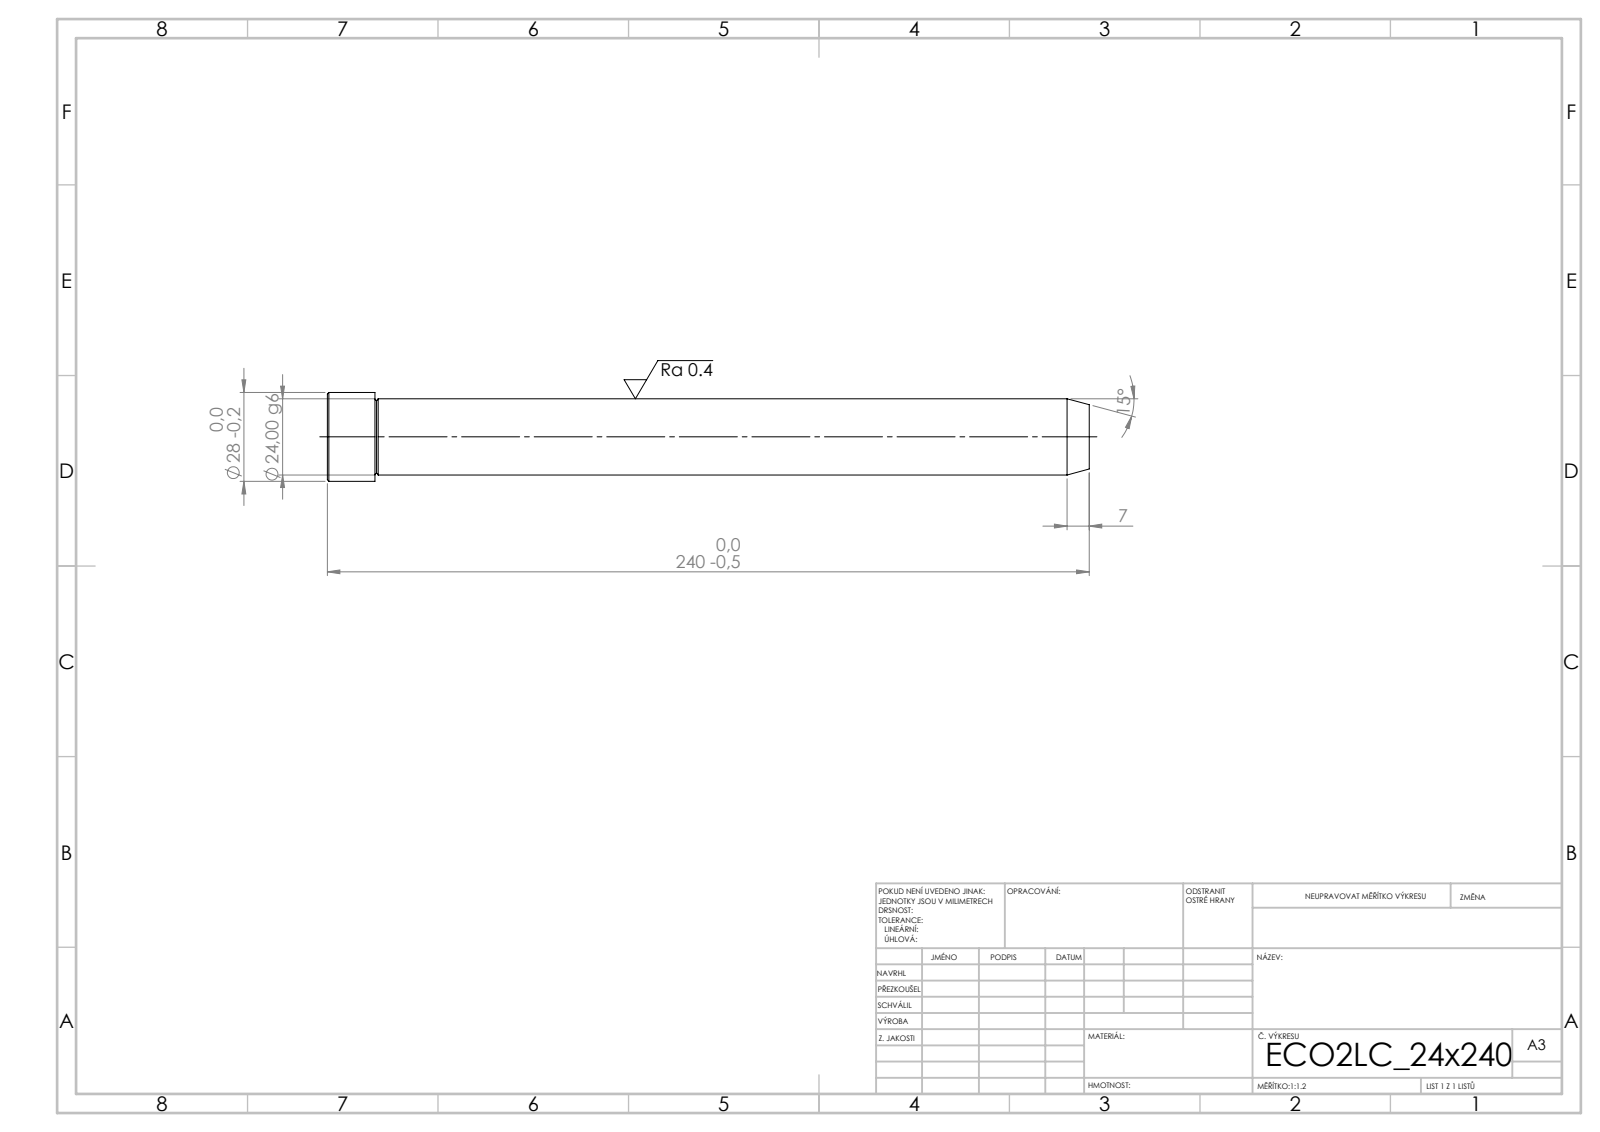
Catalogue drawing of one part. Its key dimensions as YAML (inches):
step_written_by: "SolidWorks 2019 (CONFIG_CONTROL_DESIGN)"
units: inches
bodies: {solids: 1, faces: 15, planar: 3, cylindrical: 4, other: 8}
overall_size: [9.449, 1.102, 1.102]
volume: 6.744
surface_area: 30.03
round_bosses_or_shafts:
  - {diameter: 1.102, count: 1}
  - {diameter: 0.945, count: 1}
face_to_face_distances: [9.449, 8.858, 0.591]
